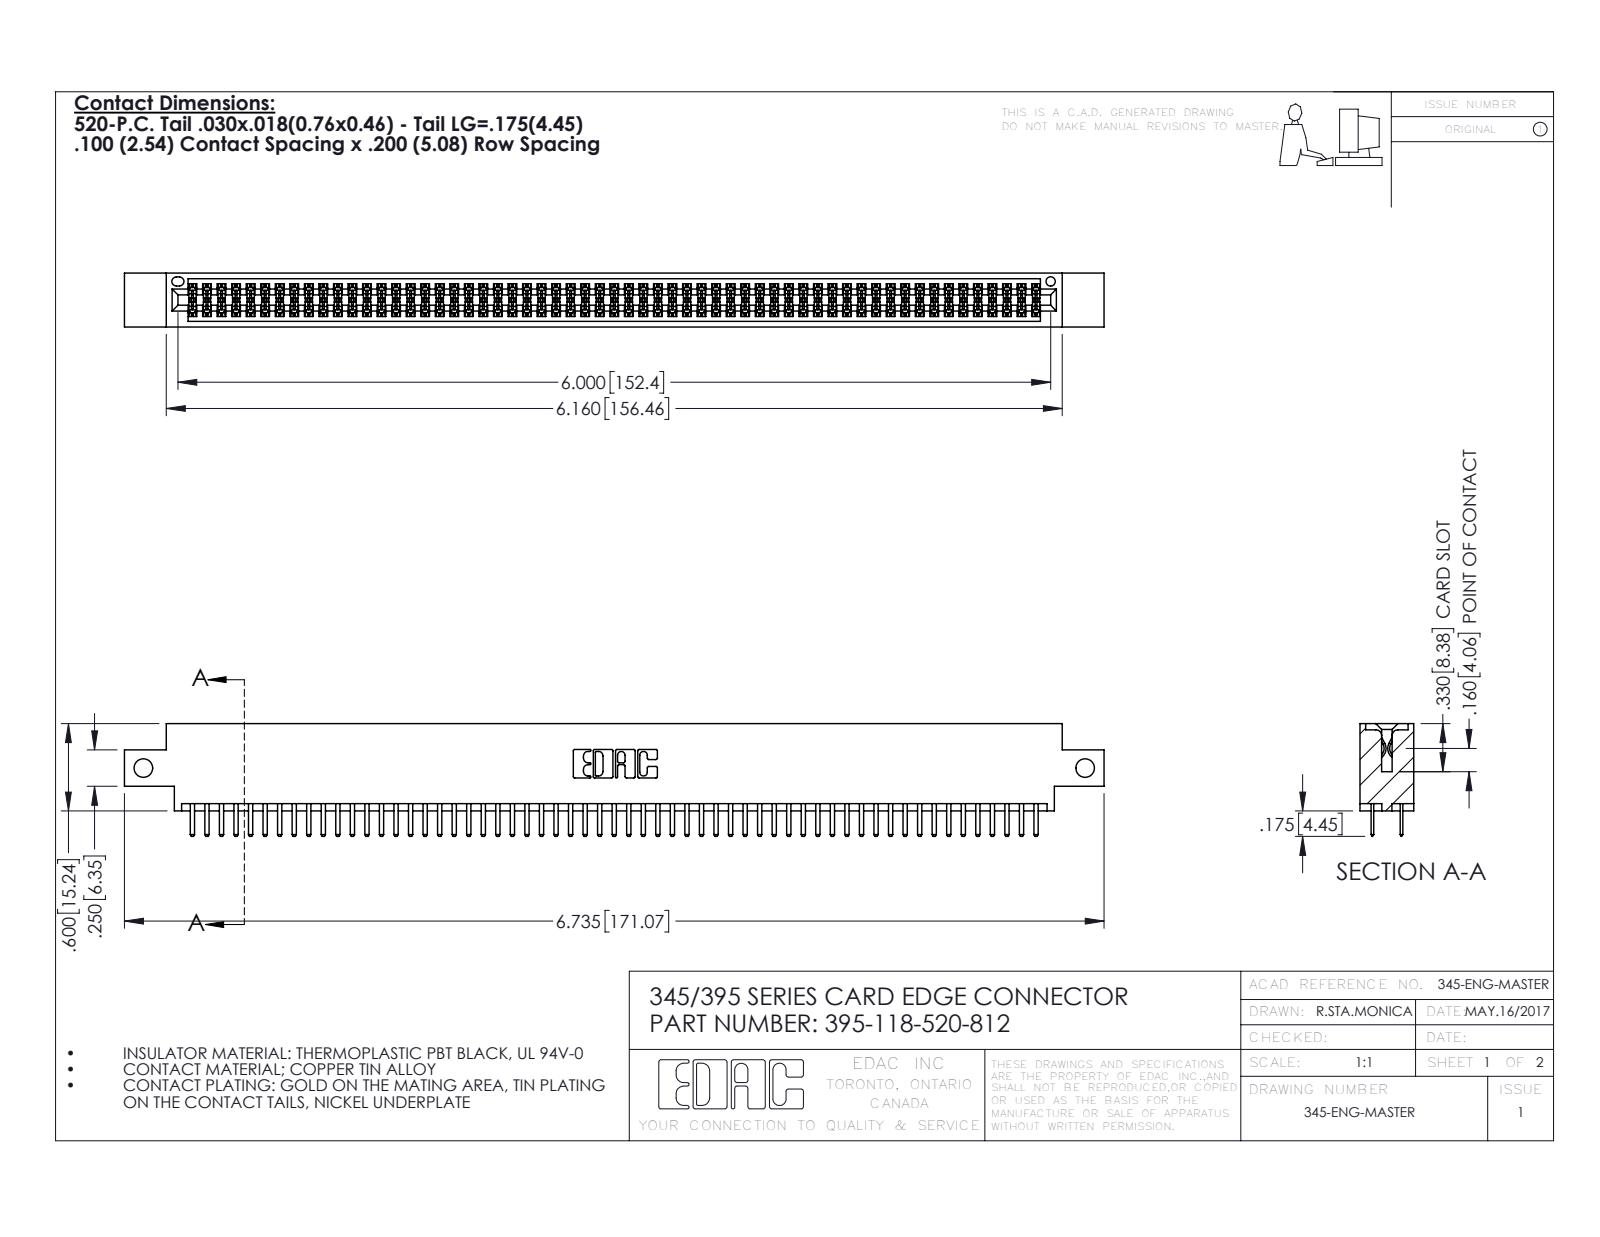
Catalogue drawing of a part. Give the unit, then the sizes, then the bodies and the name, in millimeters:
Units: millimetres
Overall size (bounding box): 171.1 × 19.7 × 9.4
Round holes (diameter × count): ⌀3.3 ×2, ⌀1.6 ×1
Partial cylindrical surfaces — rounded edges, fillets, slot ends (radius × count): R0.2 ×177, R0.3 ×122, R0.3 ×22, R0.2 ×6, R0.8 ×6, R0.7 ×3, R0.4 ×2, R0.5 ×2
Main face-to-face distances: 7.6, 1.8, 5.1, 9.4, 2.5, 6.9, 0.6, 5.7, 0.6, 1.8
Hole centre spacings: 164.5
Volume: 16 520 mm³ · Surface area: 24 650 mm²
Bodies: 119 solids, 6502 faces (4214 planar, 2288 cylindrical, 0 other)
Part name (STEP PRODUCT): 345-292-001_345-293-120; 345 Part_0.170 Offset - Side Mount; 395-118-520-812
STEP written by: SolidWorks 2016 (CONFIG_CONTROL_DESIGN)
